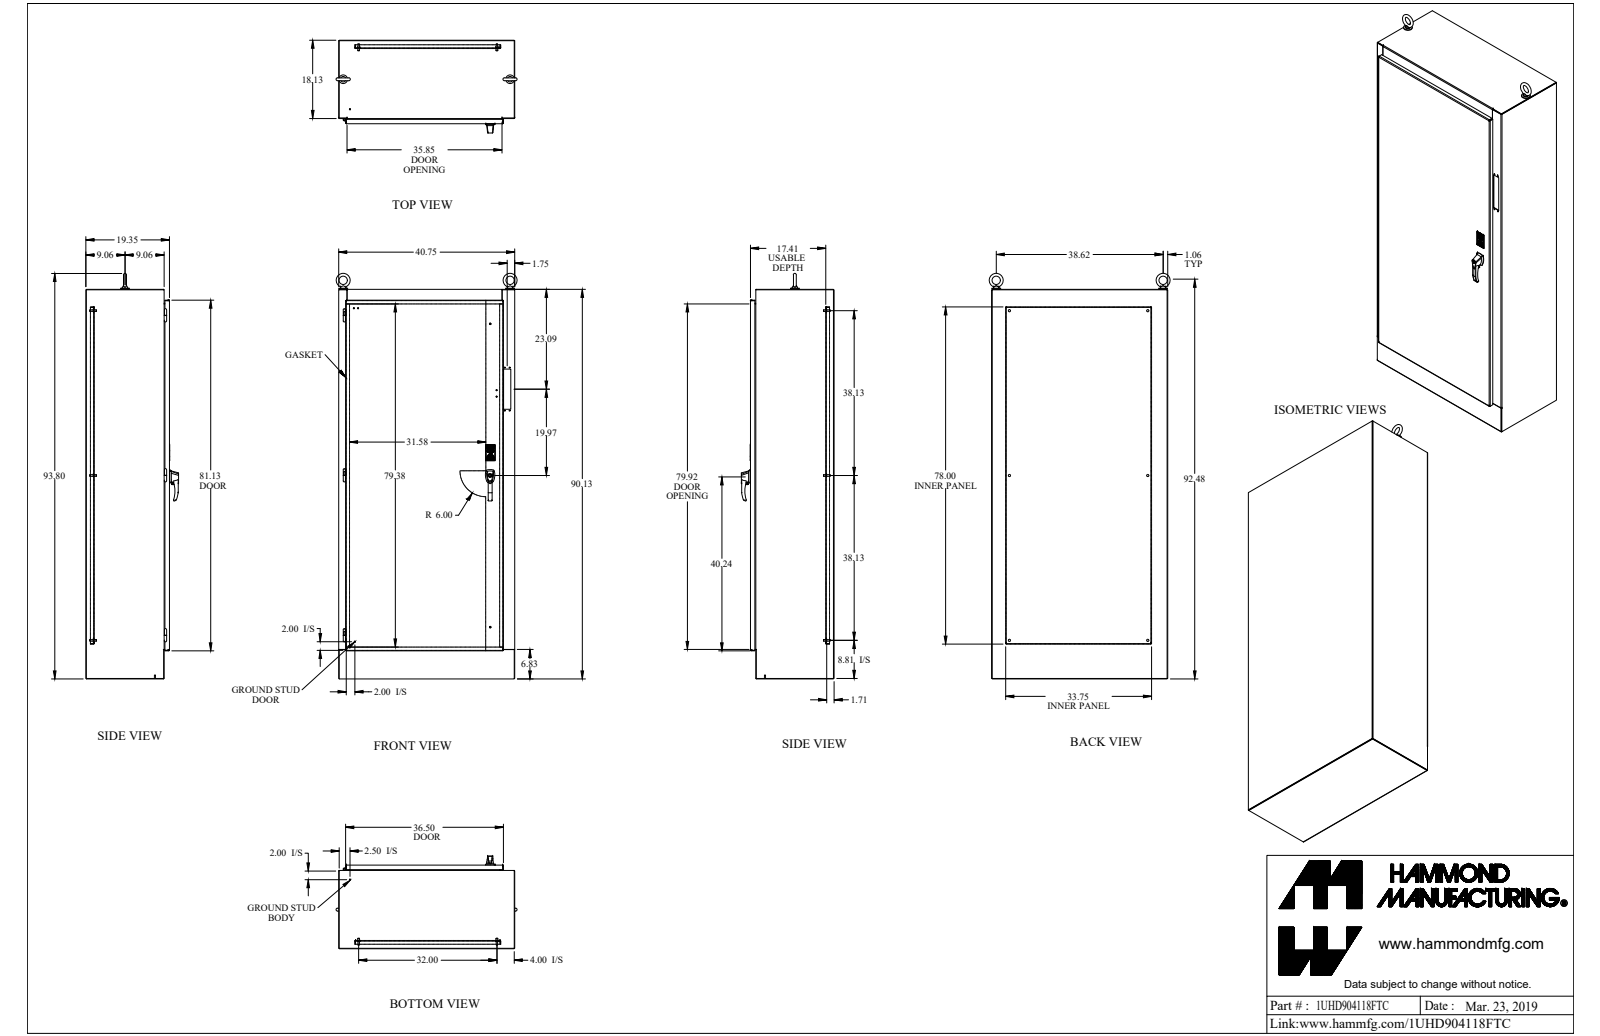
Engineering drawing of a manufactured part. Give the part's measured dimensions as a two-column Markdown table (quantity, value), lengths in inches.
| quantity | value |
| --- | --- |
| part name | 1UHD904118FTC |
| STEP written by | SolidWorks 2018 (AUTOMOTIVE_DESIGN) |
| units | inches |
| bodies | 102 solids, 1773 faces (978 planar, 482 cylindrical, 313 other) |
| overall size | 93.799 × 41.872 × 21.464 |
| volume | 2 131 in³ |
| surface area | 34 140 in² |
| round holes (diameter × count) | 0.307 × 7, 0.35 × 7, 0.281 × 6, 0.445 × 6, 0.563 × 6, 0.196 × 5, 0.25 × 3, 0.313 × 3, 0.167 × 2, 0.255 × 2, 0.257 × 2, 0.28 × 2 |
| round bosses / shafts (diameter × count) | 0.25 × 10, 1 × 8, 0.375 × 7, 0.65 × 6, 0.33 × 6, 0.281 × 4, 0.188 × 4, 0.625 × 3 |
| partial cylindrical surfaces (radius × count) | 0.06 × 39, 0.185 × 28, 0.5 × 25, 0.125 × 22, 0.017 × 16, 0.032 × 12, 0.13 × 8, 0.75 × 7 |
| main face-to-face distances | 0.125, 0.125, 17.413, 19.225, 19.1, 19.35, 19.224, 1.937, 1.812, 17.288 |
| hole center spacings | 32, 1, 1.125, 1.126, 1.287, 2, 7.5, 9.936 |
